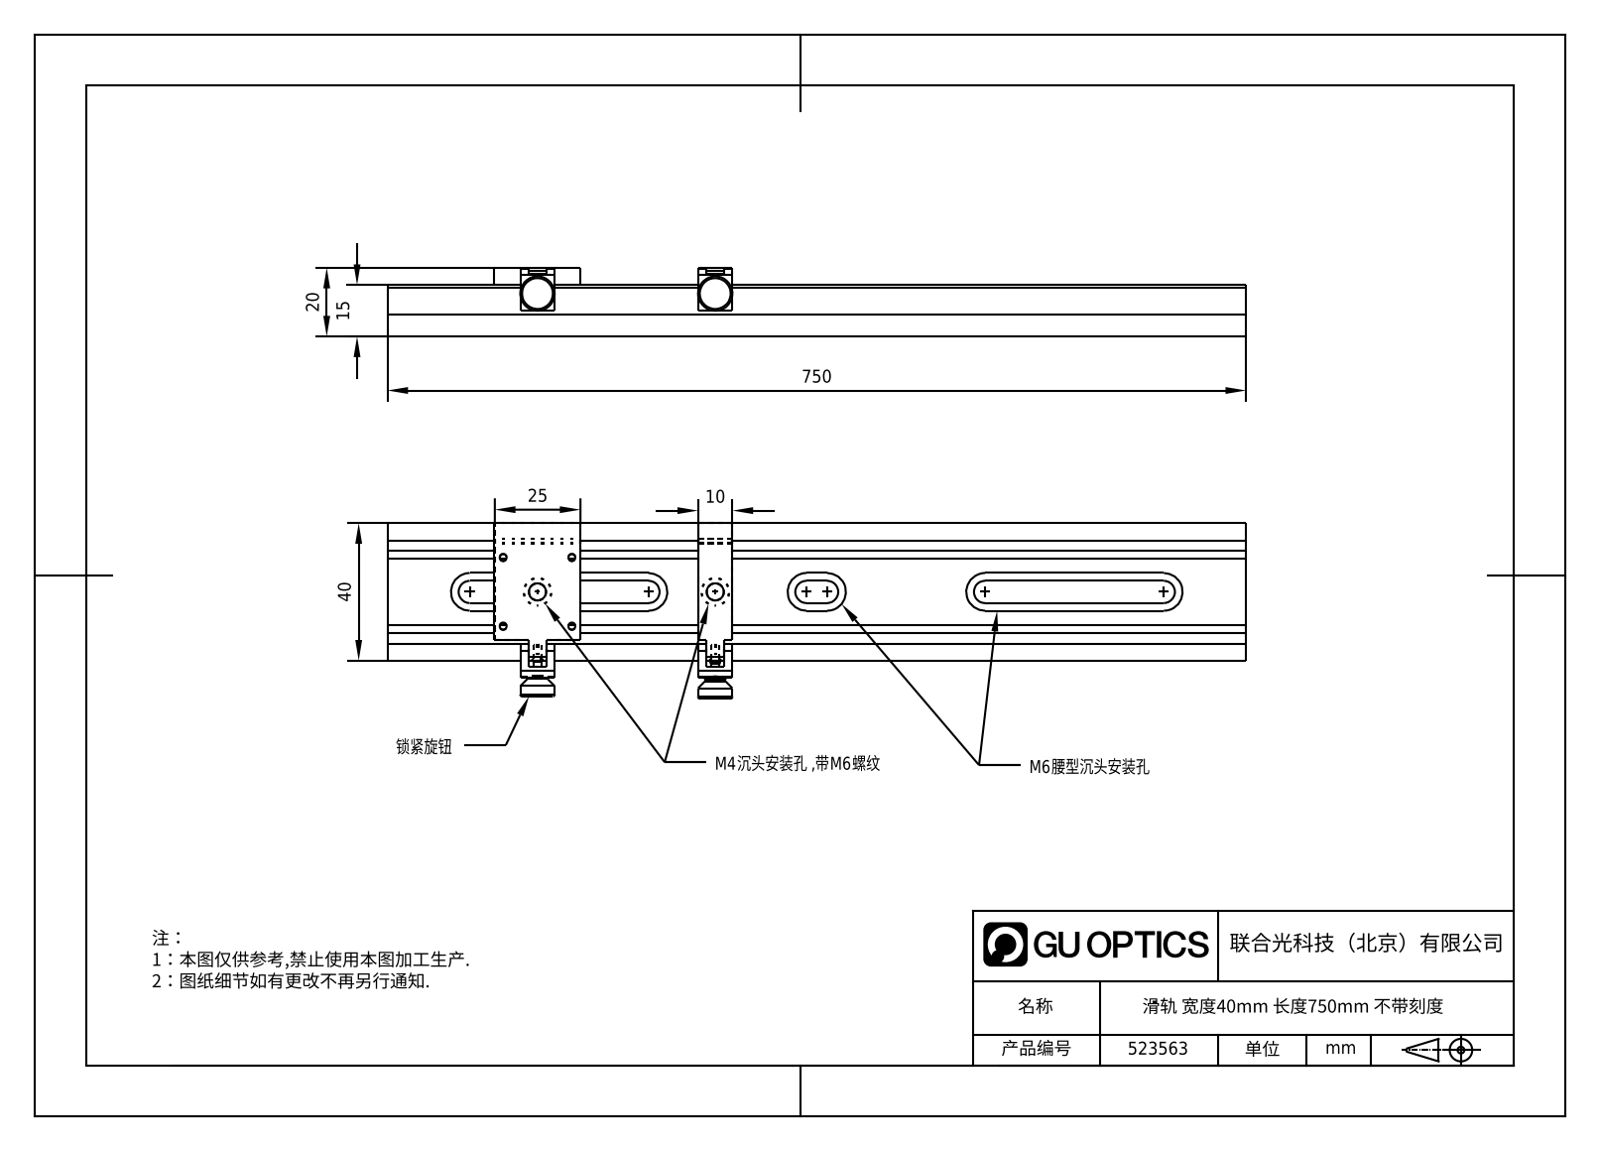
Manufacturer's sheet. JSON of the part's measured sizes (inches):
{"part_name": "4.2.1.6_H40G-750_40mm滑轨，长度750mm，附带两个H40Z滑轨安装座; 4.2.2.1，H40Z-10，40mm滑轨安装座，宽度10mm，A; 4.2.2.1.2，40mm滑轨安装座压块，宽度25mm，B; 4.2.1.6.1_40mm滑轨主体，长度750mm (+5 more)", "step_written_by": "SolidWorks 2021 (CONFIG_CONTROL_DESIGN)", "units": "inches", "bodies": {"solids": 8, "faces": 257, "planar": 130, "cylindrical": 99, "other": 28}, "overall_size": [29.528, 2.009, 0.787], "volume_in3": 17.35, "surface_area_in2": 162.5, "round_holes": [[0.081, 4], [0.098, 2], [0.126, 2], [0.197, 2], [0.315, 2], [0.059, 1], [0.079, 1]], "round_bosses_or_shafts": [[0.394, 2], [0.236, 2], [0.118, 2], [0.087, 2]], "partial_cylinders_radius": [[0.128, 14], [0.217, 14], [0.049, 1], [0.098, 1], [0.177, 1], [0.492, 1]], "face_to_face_distances": [0.236, 0.02, 0.571, 0.256, 0.591, 0.335, 1.575, 0.197, 0.315, 0.551], "hole_center_spacings": [0.557, 0.787, 1.113, 2.652, 3.017, 3.433]}
